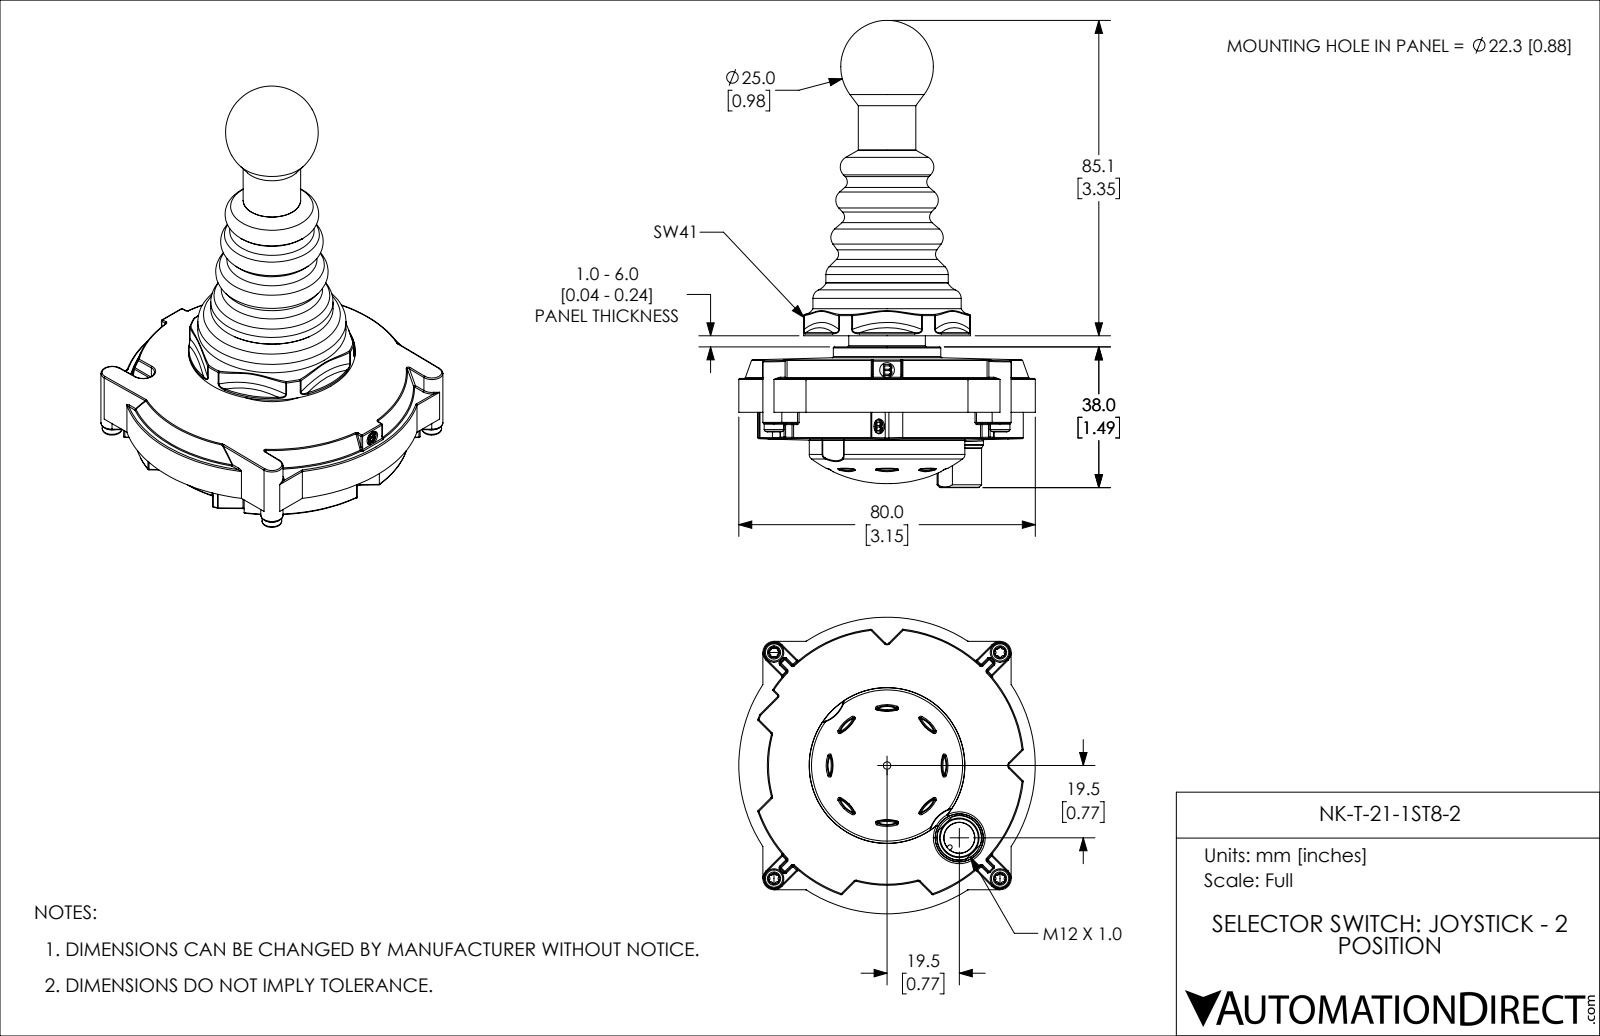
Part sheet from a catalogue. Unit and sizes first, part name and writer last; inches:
Units: inches
Overall size (bounding box): 4.961 × 3.15 × 3.15
Round holes (diameter × count): ⌀0.157 ×5, ⌀0.115 ×4, ⌀0.327 ×1, ⌀0.331 ×1, ⌀1.228 ×1, ⌀1.461 ×1, ⌀1.579 ×1
Round bosses / shafts (diameter × count): ⌀0.209 ×4, ⌀1.772 ×1, ⌀1.654 ×1, ⌀1.575 ×1, ⌀1.303 ×1, ⌀1.299 ×1, ⌀1.142 ×1, ⌀0.984 ×1
Partial cylindrical surfaces — rounded edges, fillets, slot ends (radius × count): R0.012 ×115, R0.007 ×44, R0.02 ×12, R0.102 ×8, R0.354 ×8, R0.024 ×7, R0.118 ×5, R0.027 ×2
Main face-to-face distances: 1.376, 0.555, 0.821, 2.638, 2.784, 1.963, 1.408, 1.016, 0.36, 0.461
Hole centre spacings: 2.402, 1.698, 0.177, 2.016, 2.224, 3.396, 0.613, 1.086
Volume: 10.1 in³ · Surface area: 50.22 in²
Bodies: 4 solids, 1358 faces (374 planar, 341 cylindrical, 643 other)
Part name (STEP PRODUCT): NK-T-21-1ST8-2
STEP written by: SolidWorks 2019 (CONFIG_CONTROL_DESIGN)
